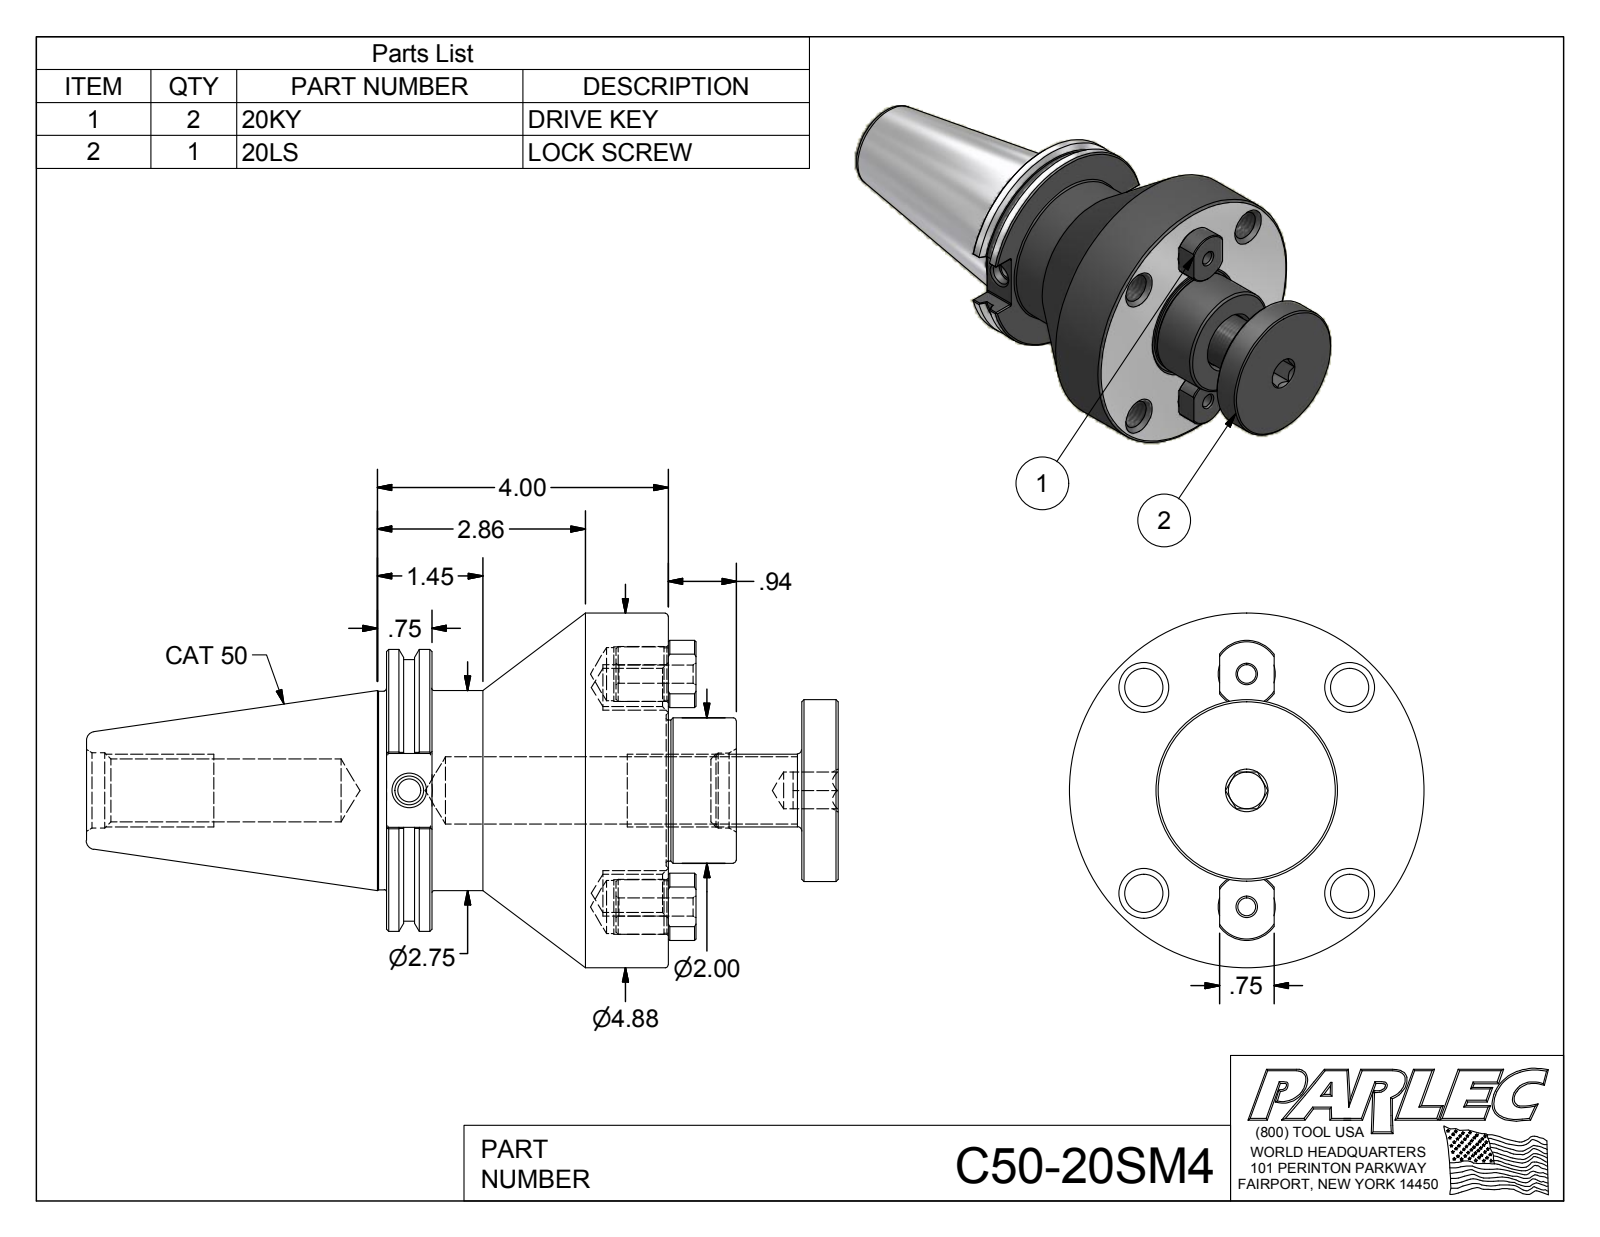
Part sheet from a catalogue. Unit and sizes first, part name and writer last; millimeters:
Units: millimetres
Overall size (bounding box): 262.5 × 123.8 × 123.8
Round holes (diameter × count): ⌀13.4 ×4, ⌀6.4 ×2, ⌀18.5 ×2, ⌀19.1 ×2, ⌀8 ×1, ⌀10.1 ×1, ⌀12.8 ×1, ⌀22 ×1, ⌀23.4 ×1, ⌀26.2 ×1, ⌀26.4 ×1
Round bosses / shafts (diameter × count): ⌀19.2 ×2, ⌀18.3 ×2, ⌀123.8 ×1, ⌀98.4 ×1, ⌀91.3 ×1, ⌀69.9 ×1, ⌀69.3 ×1, ⌀63.5 ×1
Partial cylindrical surfaces — rounded edges, fillets, slot ends (radius × count): R0.5 ×12, R11.8 ×2
Main face-to-face distances: 59.3, 98.4, 157.7, 15.9, 82.6, 141.9, 145, 129.2, 46.6, 12.7
Hole centre spacings: 36.2, 50.8, 71.8, 84.6, 40.6, 101.6, 81.3
Volume: 1 060 000 mm³ · Surface area: 115 200 mm²
Bodies: 4 solids, 174 faces (57 planar, 50 cylindrical, 67 other)
Part name (STEP PRODUCT): C50-20SM4; C50-20SM4-1; 20KY; 20LS
STEP written by: Autodesk Inventor 2012 (AUTOMOTIVE_DESIGN)
